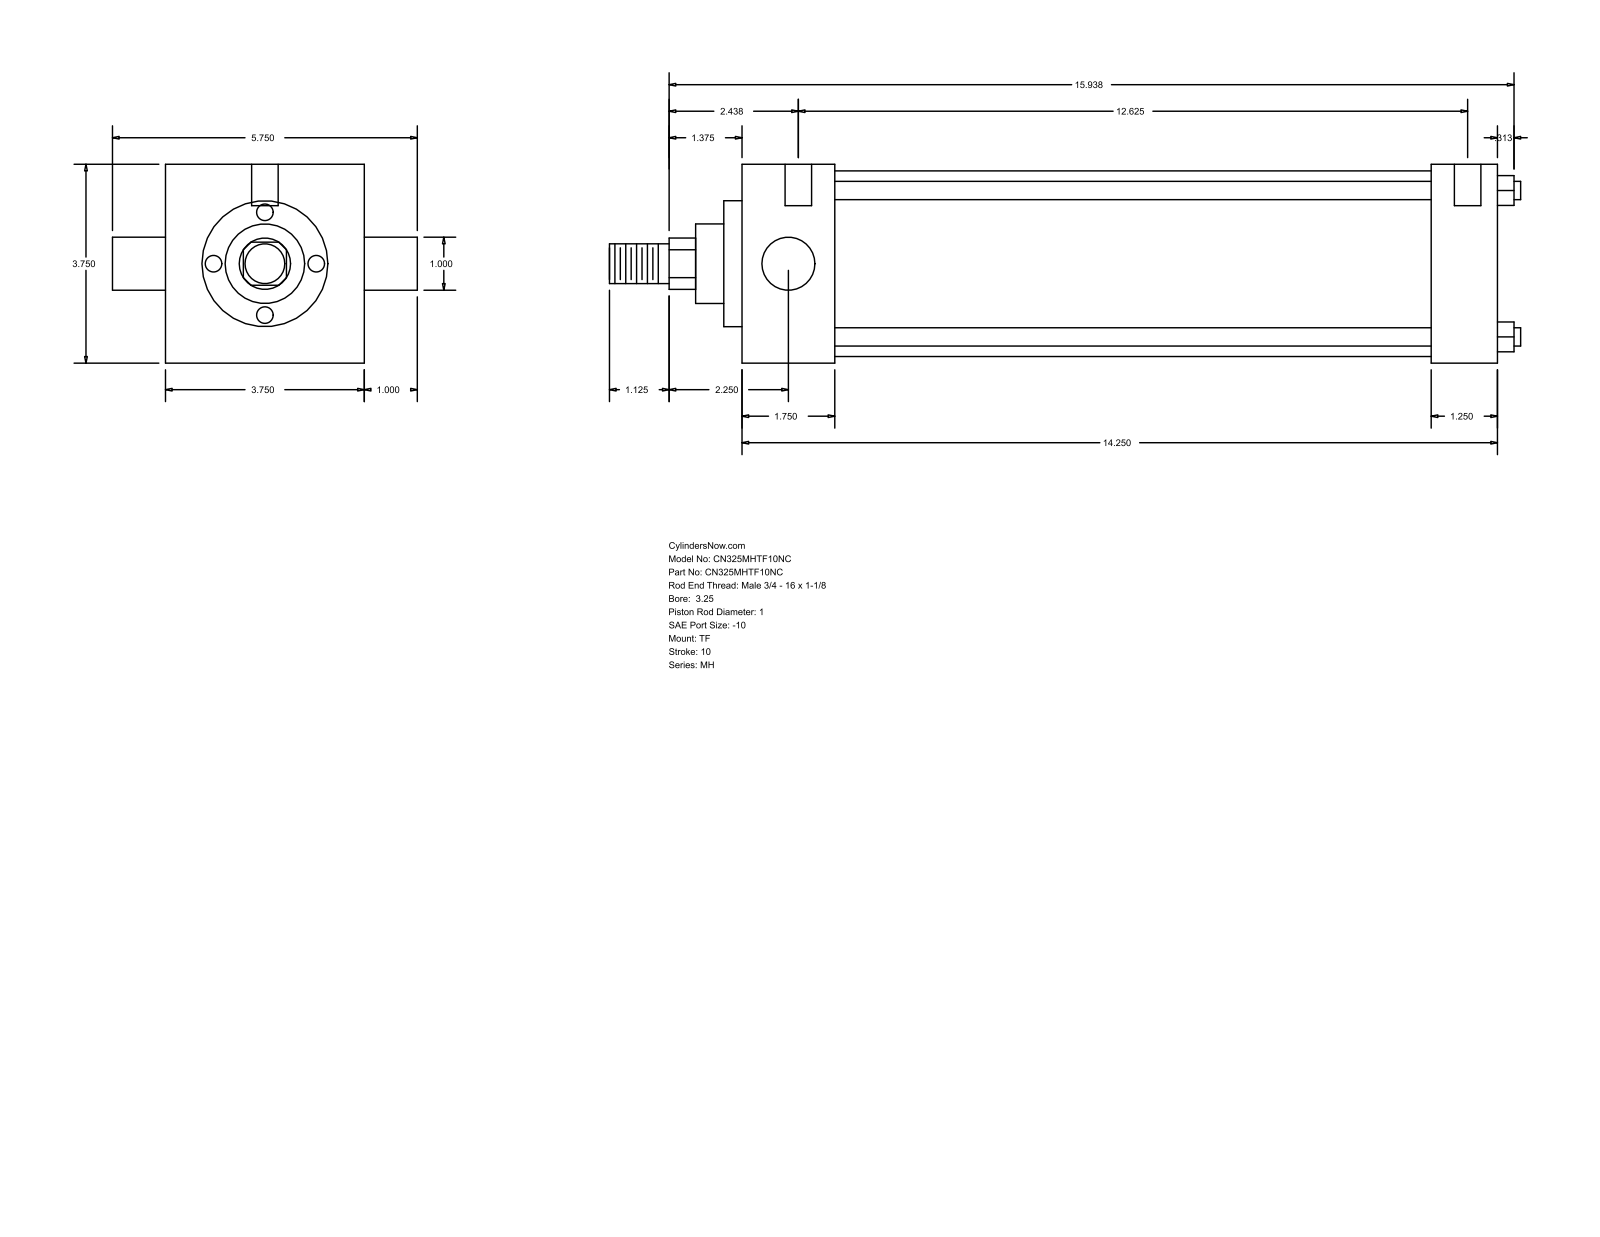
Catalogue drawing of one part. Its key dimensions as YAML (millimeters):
part_name: "MH_TF__0325_1"
step_written_by: "GSSL Pune (CONFIG_CONTROL_DESIGN)"
units: millimeters
bodies: {solids: 0, faces: 86, planar: 61, cylindrical: 25, other: 0}
overall_size: [436.56, 146.05, 95.25]
round_holes:
  - {diameter: 5.56, count: 3}
  - {diameter: 12.7, count: 2}
round_bosses_or_shafts:
  - {diameter: 8.76, count: 4}
  - {diameter: 25.4, count: 2}
  - {diameter: 88.9, count: 1}
  - {diameter: 60.33, count: 1}
  - {diameter: 38.1, count: 1}
  - {diameter: 19.05, count: 1}
partial_cylinders:
  - {radius: 12.29, count: 1}
face_to_face_distances: [95.24, 361.96, 44.46, 330.2, 285.74, 317.5, 31.76, 8.73, 53.19, 338.93]
hole_center_spacings: [1.58, 4.76, 320.68, 322.26, 325.44, 327.02]
